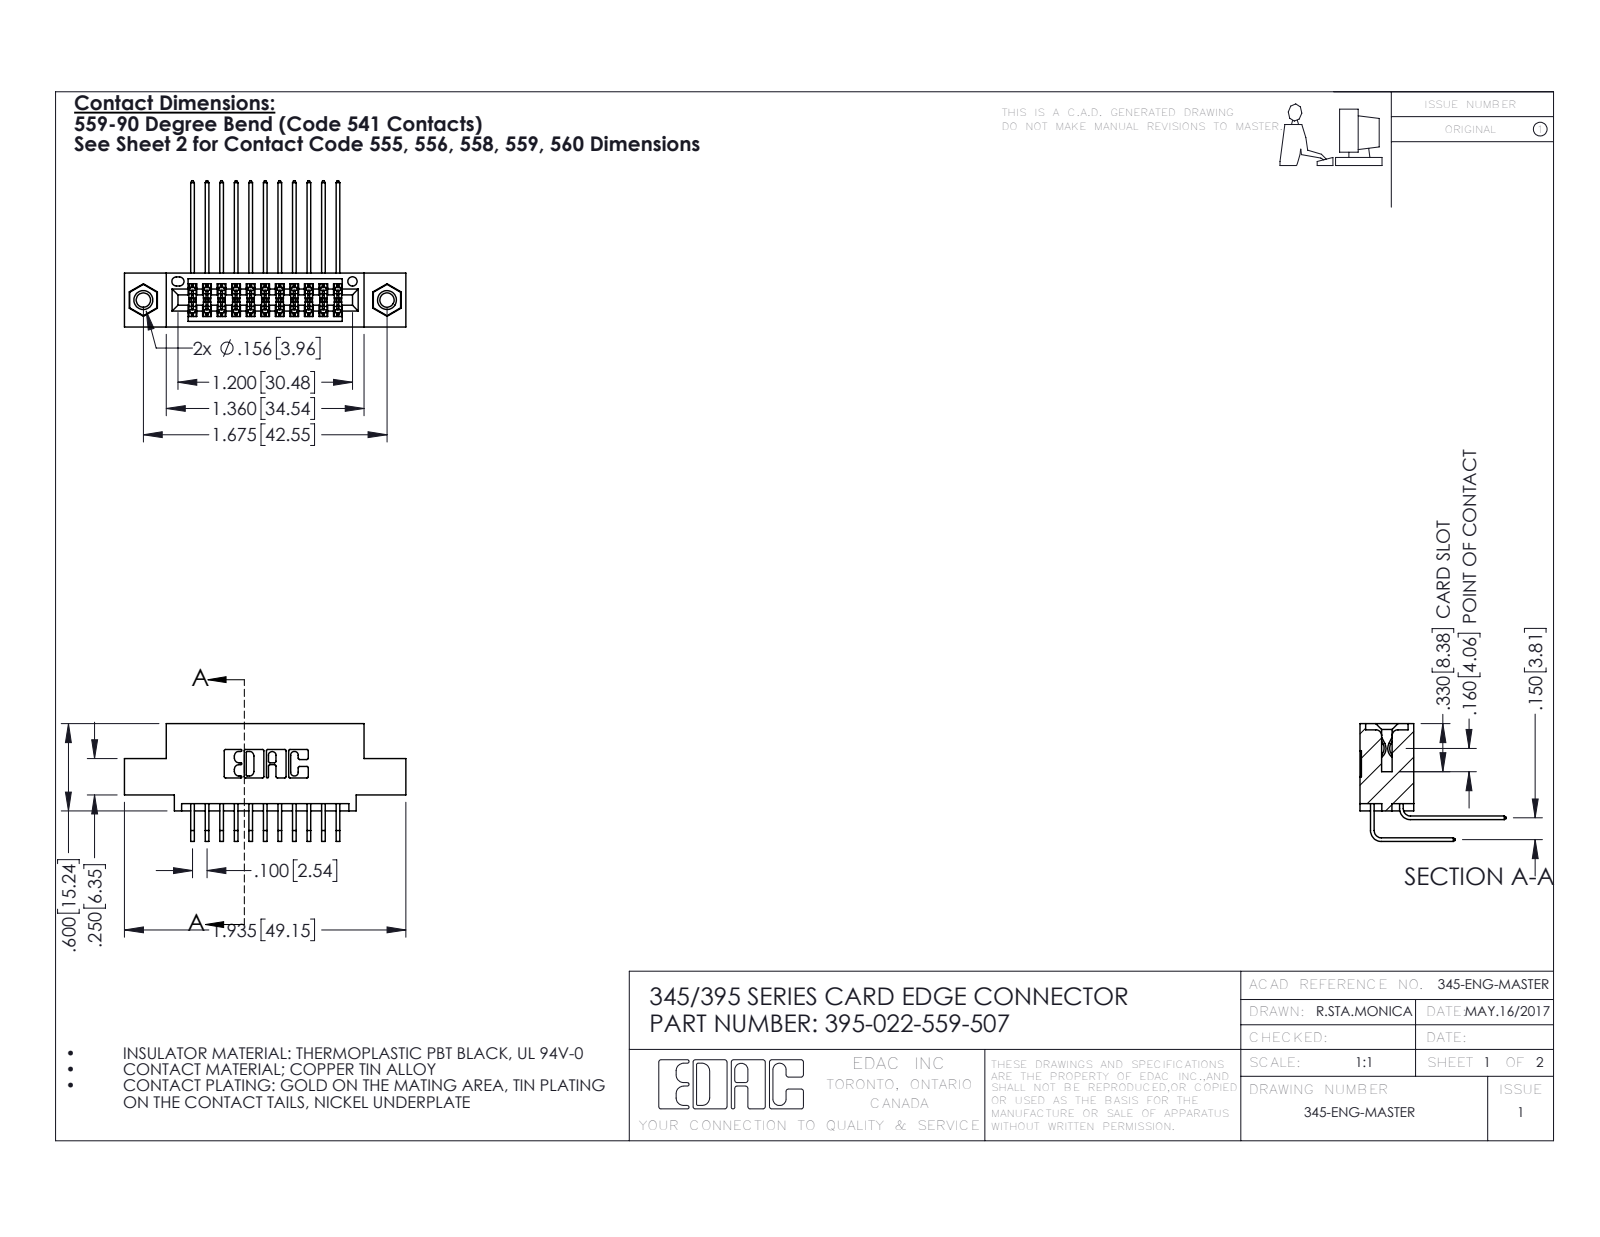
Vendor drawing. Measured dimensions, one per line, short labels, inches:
name: 395-022-559-507; 345-292-001_558 559 Tail - 1; 345-292-001_559 Tail - 2; 345-250-001_345-250-005-103 (+1 more)
written by: SolidWorks 2016 (CONFIG_CONTROL_DESIGN)
unit: in
bodies: 25 solids, 1334 faces (886 planar, 432 cylindrical, 16 other)
size: 1.935 × 1.005 × 0.809
volume: 0.276 in³; area: 10.55 in²
holes: 2× ⌀0.098, 2× ⌀0.125, 2× ⌀0.156, 1× ⌀0.064
bosses: 2× ⌀0.155
rounds: 33× R0.006, 22× R0.01, 6× R0.007, 6× R0.031, 3× R0.026, 2× R0.014, 2× R0.019, 2× R0.022
face distances: 0.2, 0.072, 0.298, 0.37, 0.098, 0.272, 0.025, 0.15, 0.225, 0.1
hole spacings: 0.27, 1.443, 1.675
